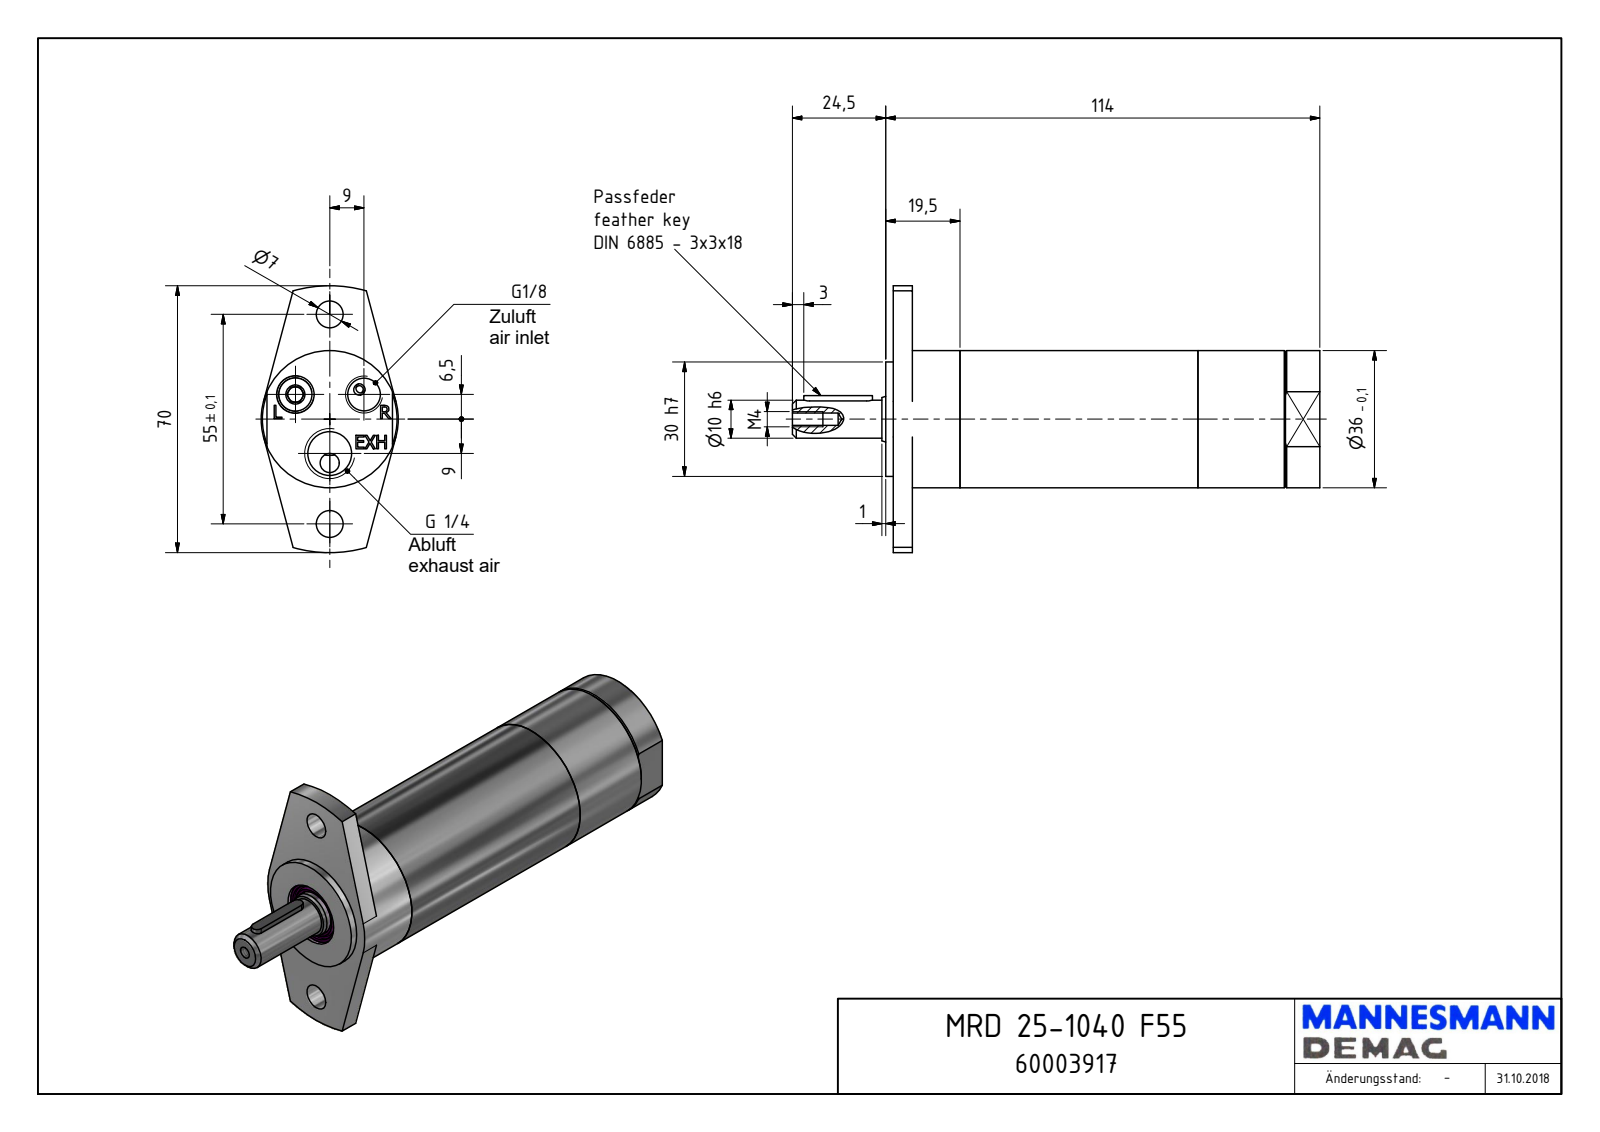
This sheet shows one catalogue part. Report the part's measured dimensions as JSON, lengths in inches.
{"part_name": "MRD 25-1040 F55_60003917", "step_written_by": "Autodesk Inventor 2018 (AUTOMOTIVE_DESIGN)", "units": "inches", "bodies": {"solids": 1, "faces": 140, "planar": 96, "cylindrical": 21, "other": 23}, "overall_size": [5.453, 2.756, 1.417], "volume_in3": 7.24, "surface_area_in2": 30.19, "round_holes": [[0.276, 2], [0.337, 2], [0.128, 1], [0.157, 1], [0.451, 1], [0.61, 1], [0.669, 1]], "round_bosses_or_shafts": [[1.417, 1], [1.181, 1], [0.47, 1], [0.394, 1]], "partial_cylinders_radius": [[0.059, 2], [1.378, 1]], "face_to_face_distances": [0.197, 4.213, 4.409, 0.079, 0.276, 4.488, 3.987, 3.909, 3.712, 0.501], "hole_center_spacings": [0.437, 0.706, 0.9, 1.083, 1.385, 0.354, 0.709, 0.728]}
